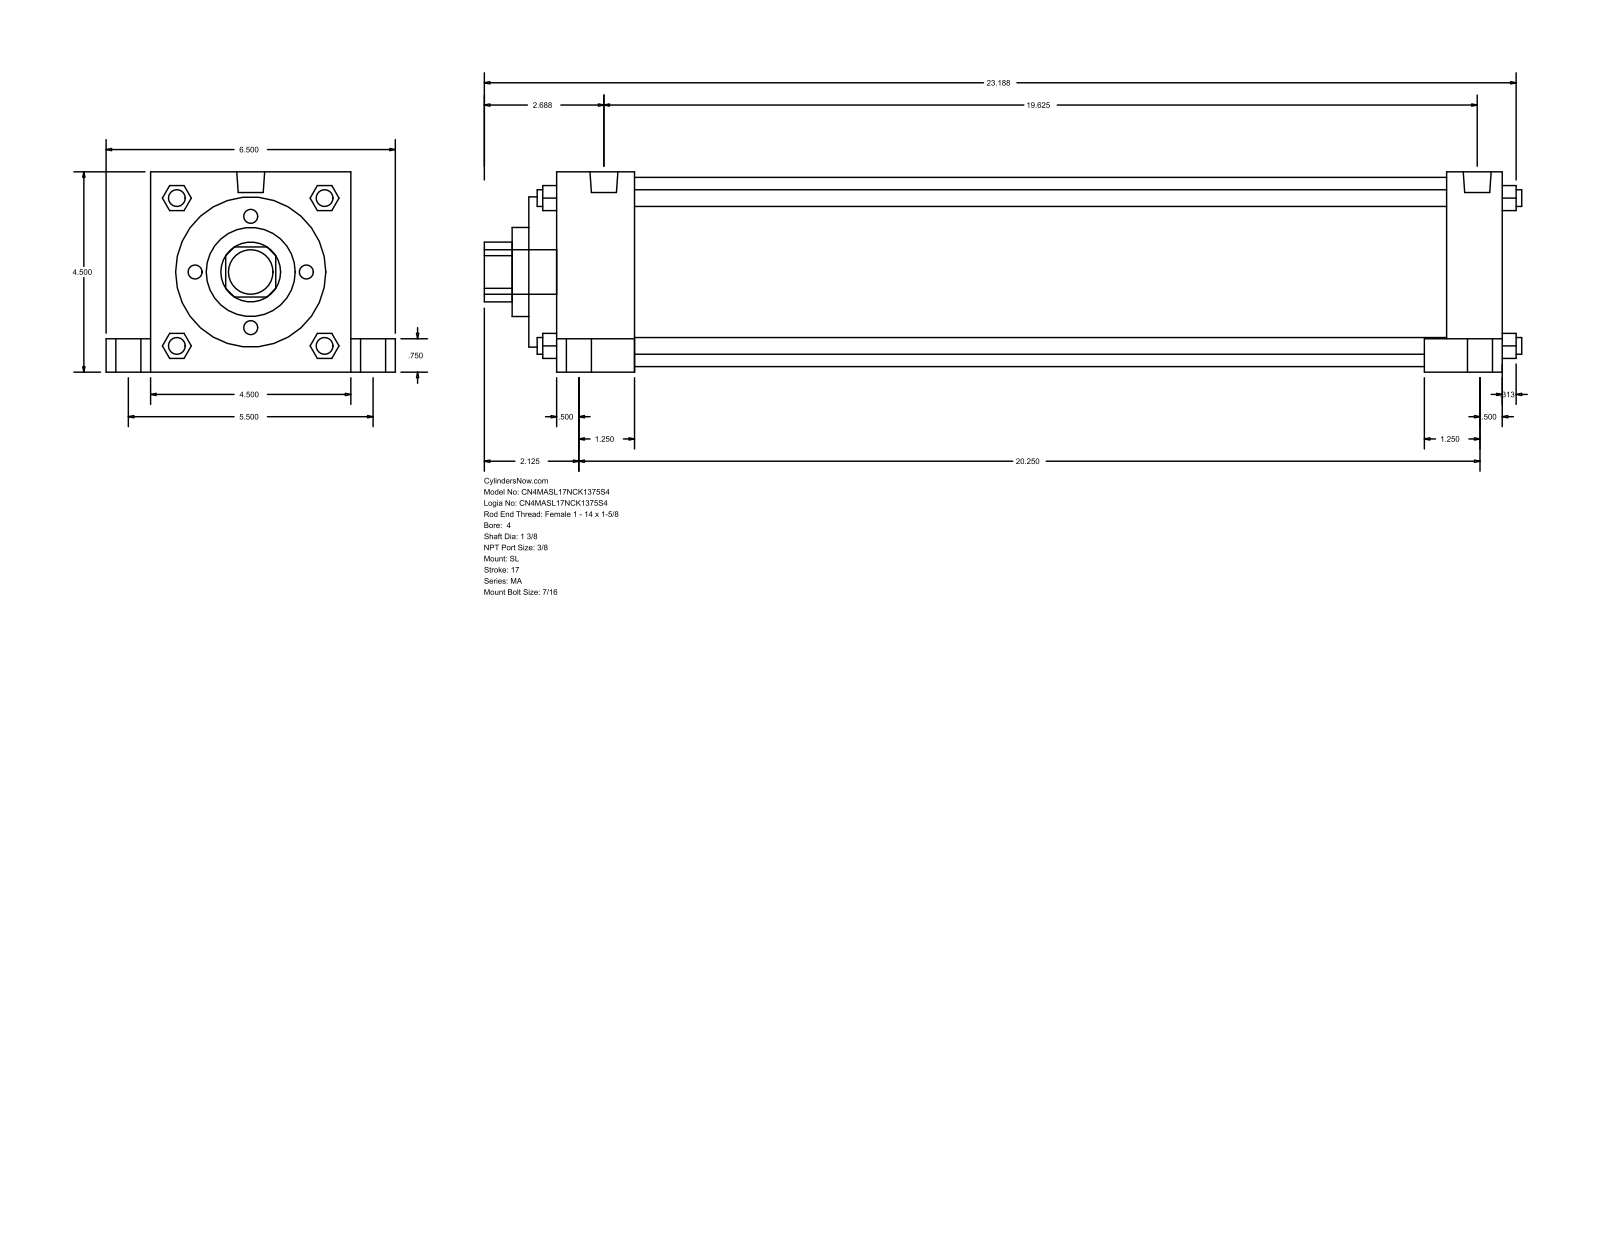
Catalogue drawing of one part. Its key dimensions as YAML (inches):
part_name: "MA_SL__0400_1.375"
step_written_by: "GSSL Pune (CONFIG_CONTROL_DESIGN)"
units: inches
bodies: {solids: 0, faces: 150, planar: 113, cylindrical: 37, other: 0}
overall_size: [23.313, 6.5, 4.5]
round_holes:
  - {diameter: 1.375, count: 1}
  - {diameter: 2, count: 1}
  - {diameter: 3.375, count: 1}
  - {diameter: 4.25, count: 1}
round_bosses_or_shafts:
  - {diameter: 0.813, count: 4}
  - {diameter: 0.563, count: 4}
  - {diameter: 0.437, count: 4}
  - {diameter: 0.375, count: 4}
  - {diameter: 0.627, count: 2}
  - {diameter: 1, count: 1}
partial_cylinders:
  - {radius: 0.672, count: 1}
face_to_face_distances: [4.5, 21.25, 18.25, 21.875, 0.625, 2.375, 1.75, 19.5, 20.625, 20]
